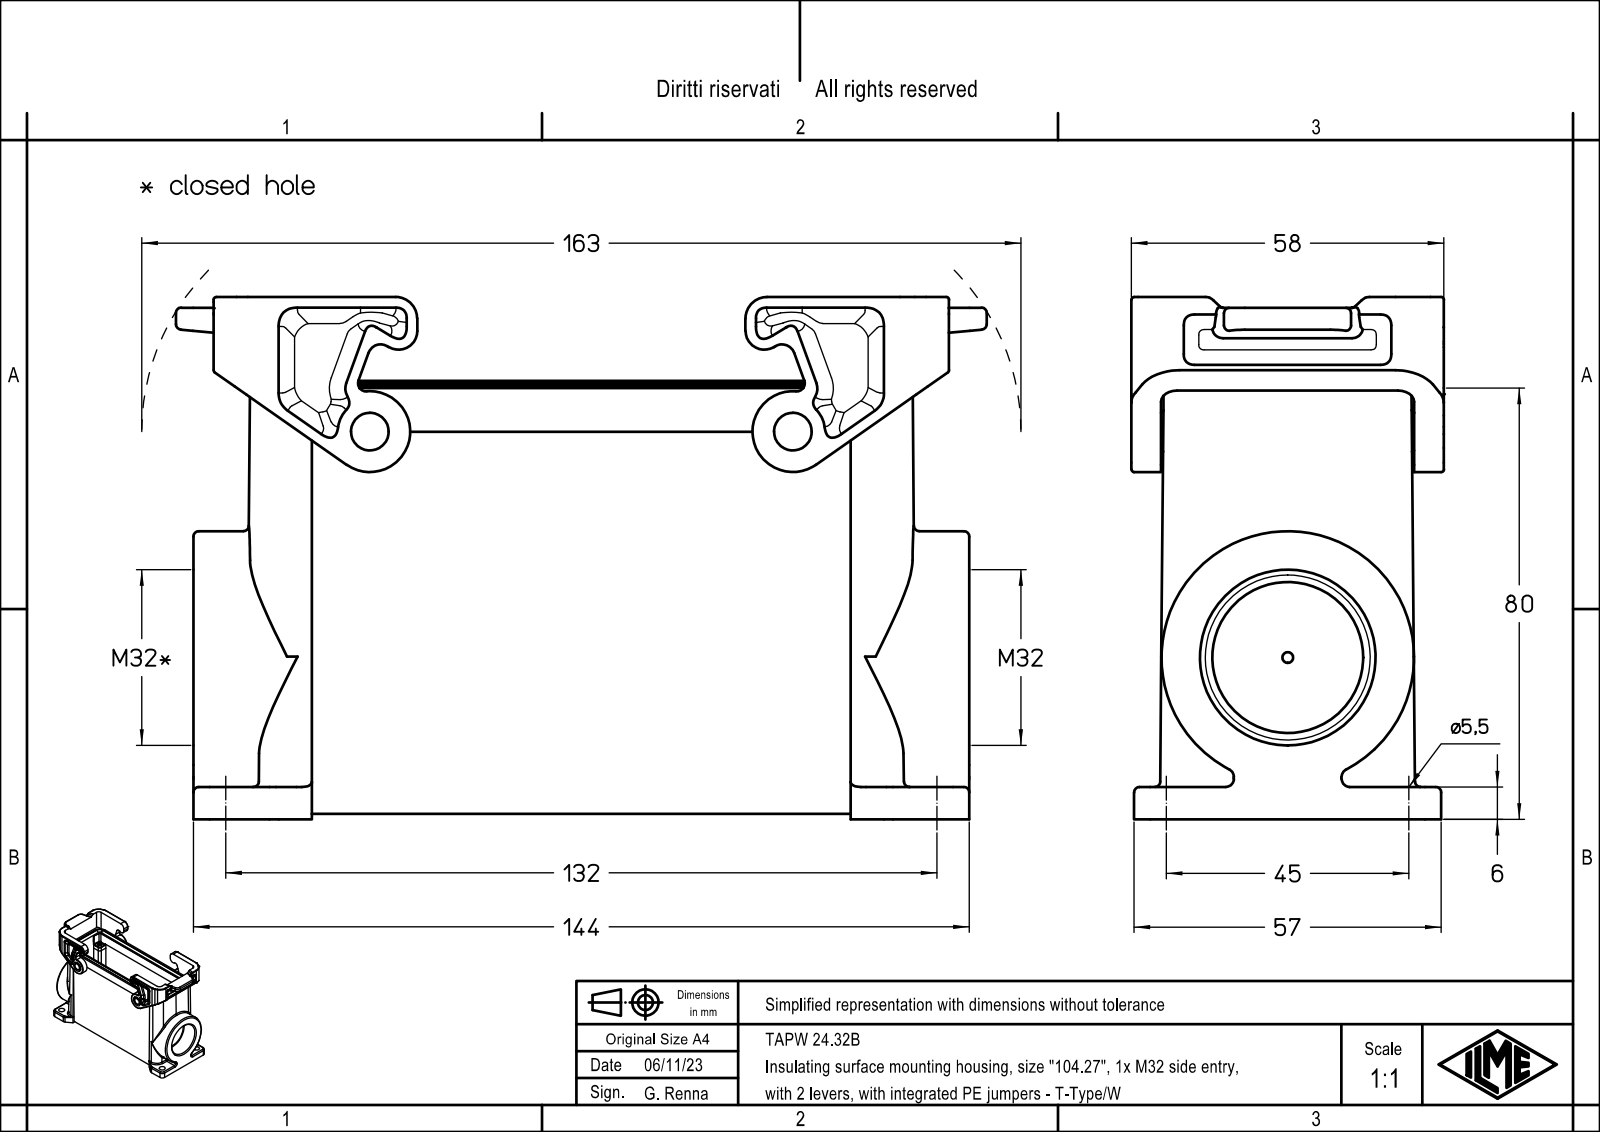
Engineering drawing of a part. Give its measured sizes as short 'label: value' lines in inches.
name: TAPW 24.32B
written by: Creo Elements/Direct Modeling 20.1B 02-Apr-2019 (C) Parametric Technology GmbH (AUTOMOTIVE_DESIGN)
unit: in
bodies: 1 solid, 606 faces (360 planar, 194 cylindrical, 52 other)
size: 5.925 × 3.815 × 2.283
volume: 14 in³; area: 132.3 in²
holes: 4× ⌀0.138, 4× ⌀0.217, 1× ⌀1.102, 1× ⌀1.205
bosses: 2× ⌀0.276, 1× ⌀1.845
rounds: 20× R0.079, 20× R0.118, 18× R0.059, 16× R0.039, 12× R0.051, 8× R0.236, 8× R0.276, 6× R0.157
face distances: 1.386, 0.217, 0.232, 1.618, 0.039, 0.256, 0.248, 0.26, 1.591, 1.602
hole spacings: 0.655, 1.521, 4.659, 4.857, 1.063, 1.772, 4.094, 4.23
